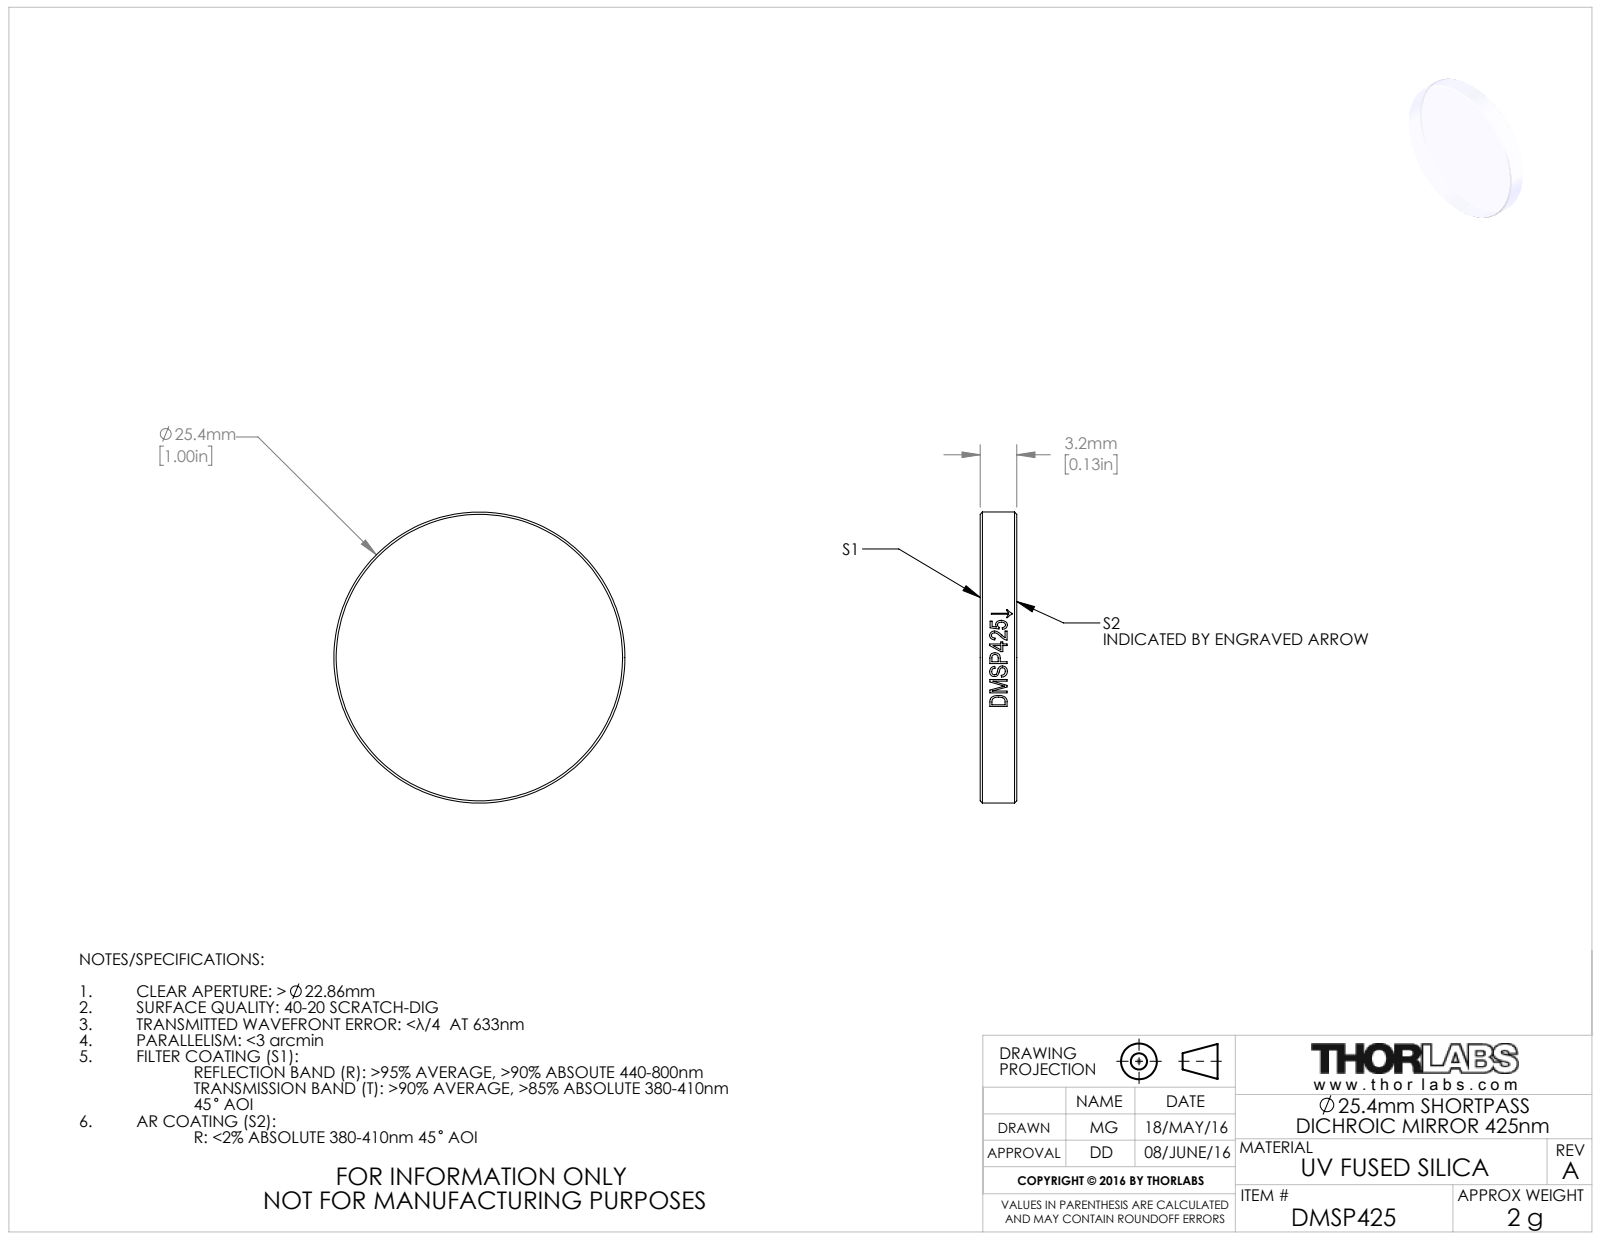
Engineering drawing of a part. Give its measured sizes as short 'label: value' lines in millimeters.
name: TTN045146-E0W
written by: SolidWorks 2016 (CONFIG_CONTROL_DESIGN)
unit: mm
bodies: 1 solid, 19 faces (2 planar, 13 cylindrical, 4 other)
size: 25.4 × 25.4 × 3.2
volume: 1 618 mm³; area: 1 250 mm²
bosses: 1× ⌀25.4
face distances: 3.2
